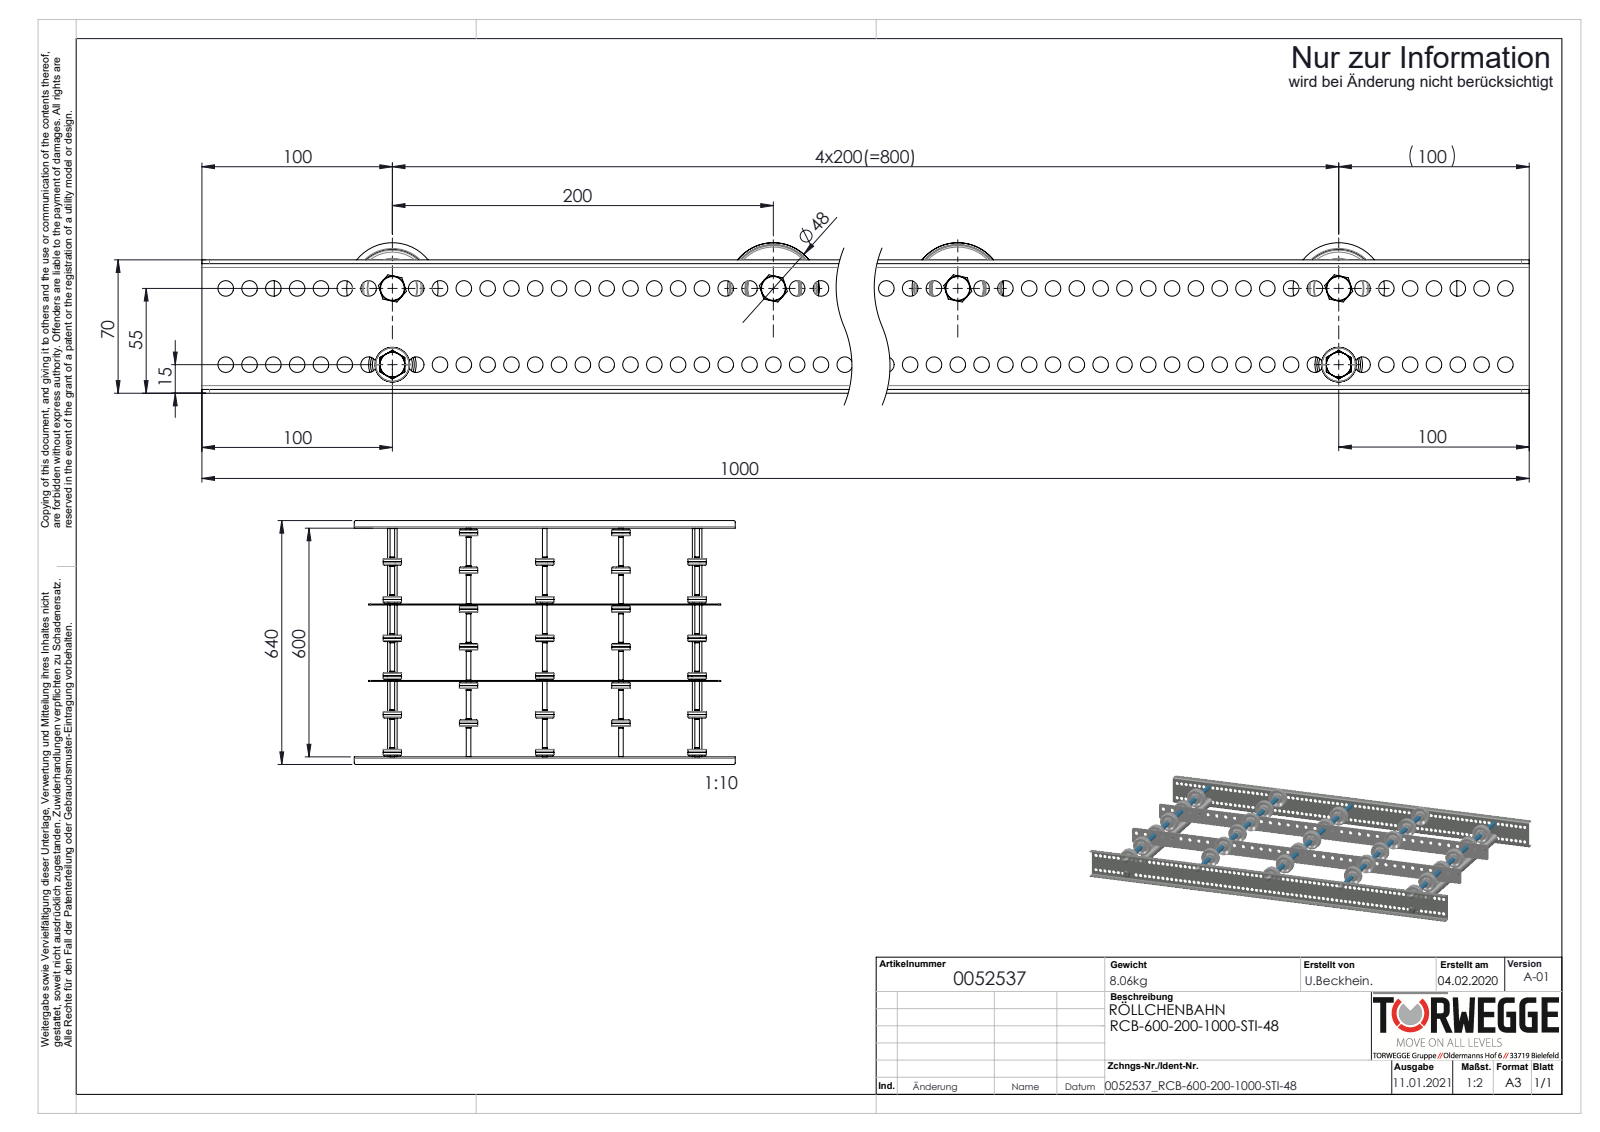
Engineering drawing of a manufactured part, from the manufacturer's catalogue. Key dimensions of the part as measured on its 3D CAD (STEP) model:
Part name (STEP PRODUCT): Hutmutter_DIN_1587_M8; 0046278_KB-ROHR-12X1,75mm_KFG_L75; S100100_Längstraverse-42x2,5_S100101_Lngstraverse-RB-L975; Traversen_KFG_L600 (+6 more)
STEP written by: SolidWorks 2020 (AUTOMOTIVE_DESIGN)
Units: millimetres
Bodies: 119 solids, 3980 faces (762 planar, 1794 cylindrical, 1424 other)
Overall size (bounding box): 1000 × 640 × 79
Volume: 1 648 000 mm³ · Surface area: 1 362 000 mm²
Round holes (diameter × count): ⌀8.2 ×158, ⌀8.5 ×37, ⌀6.65 ×5, ⌀8 ×5, ⌀9.65 ×5, ⌀15 ×5, ⌀41 ×5, ⌀6.8 ×2, ⌀21 ×2
Round bosses / shafts (diameter × count): ⌀48 ×5, ⌀13 ×5, ⌀12.5 ×5, ⌀12.4 ×5, ⌀12 ×5, ⌀11.5 ×5, ⌀25 ×2, ⌀8 ×2
Partial cylindrical surfaces — rounded edges, fillets, slot ends (radius × count): R4 ×8, R2 ×4, R5 ×4
Main face-to-face distances: 200.5, 2, 602, 2.5, 198, 401, 68, 604, 600, 99
Hole centre spacings: 12.5, 25, 37.5, 50, 62.5, 75, 87.5, 100
